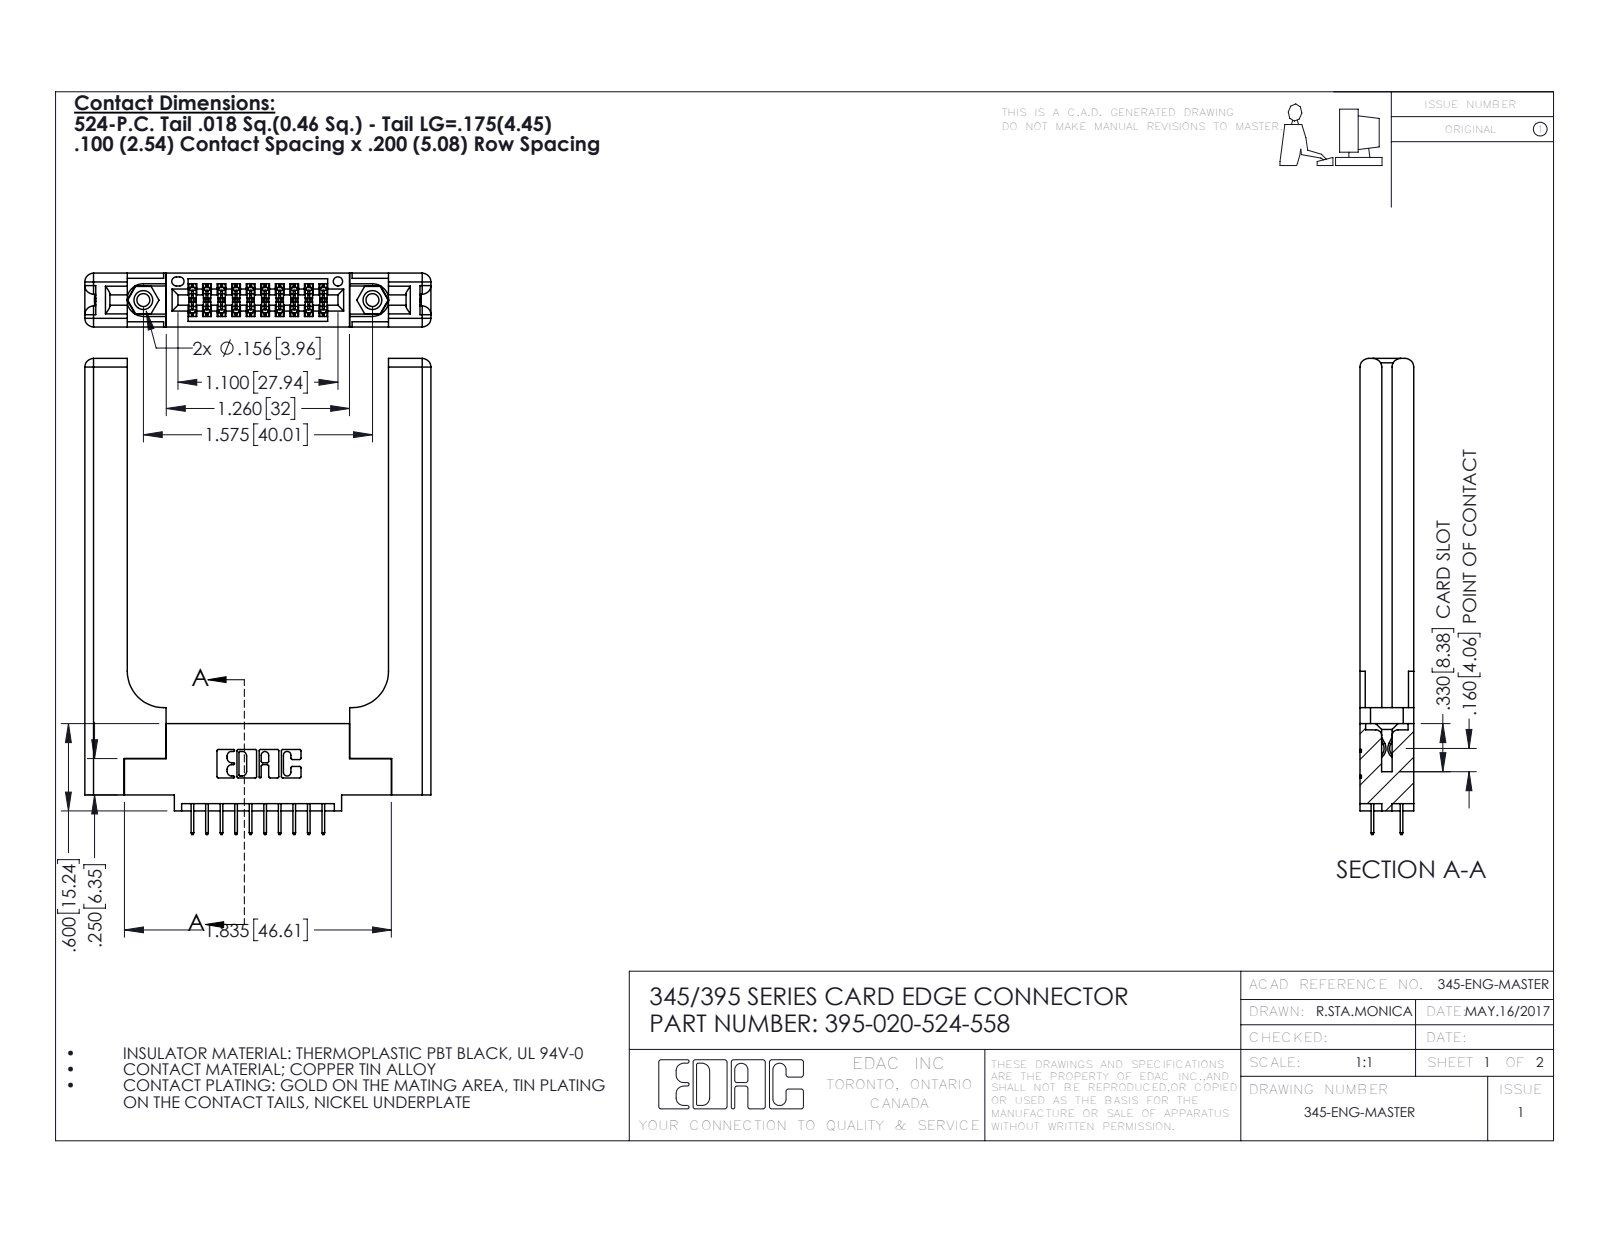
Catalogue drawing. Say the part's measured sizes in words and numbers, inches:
The part is named "395-020-524-558; 345 Part_0.110 Offset - 0.156 Dia-TH; 345-250-001_345-250-001-102; 345-292-001_345-293-124 (+1 more)". Its 3-D file was written by "SolidWorks 2016 (CONFIG_CONTROL_DESIGN)". It is 25 solids with 1466 faces: 1012 planar, 394 cylindrical and 60 other. Overall it measures 3.272 by 2.379 by 0.37 inches. Its volume is 0.851 cubic inches and its surface area 19.43 square inches. Round holes: 2 of diameter 0.089, 2 of diameter 0.125, 2 of diameter 0.156, 1 of diameter 0.064. Round bosses or shafts: 2 of diameter 0.155. Partial cylindrical surfaces (rounded edges, fillets, slot ends): 30 of radius 0.006, 22 of radius 0.01, 16 of radius 0.06, 6 of radius 0.007, 6 of radius 0.031, 3 of radius 0.026, 2 of radius 0.014, 2 of radius 0.019. The main face-to-face distances are 0.37, 0.072, 0.15, 0.22, 0.077, 0.148, 0.298, 1.796, 0.225, 0.071. The hole center spacings are 0.27, 1.344, 1.575.
